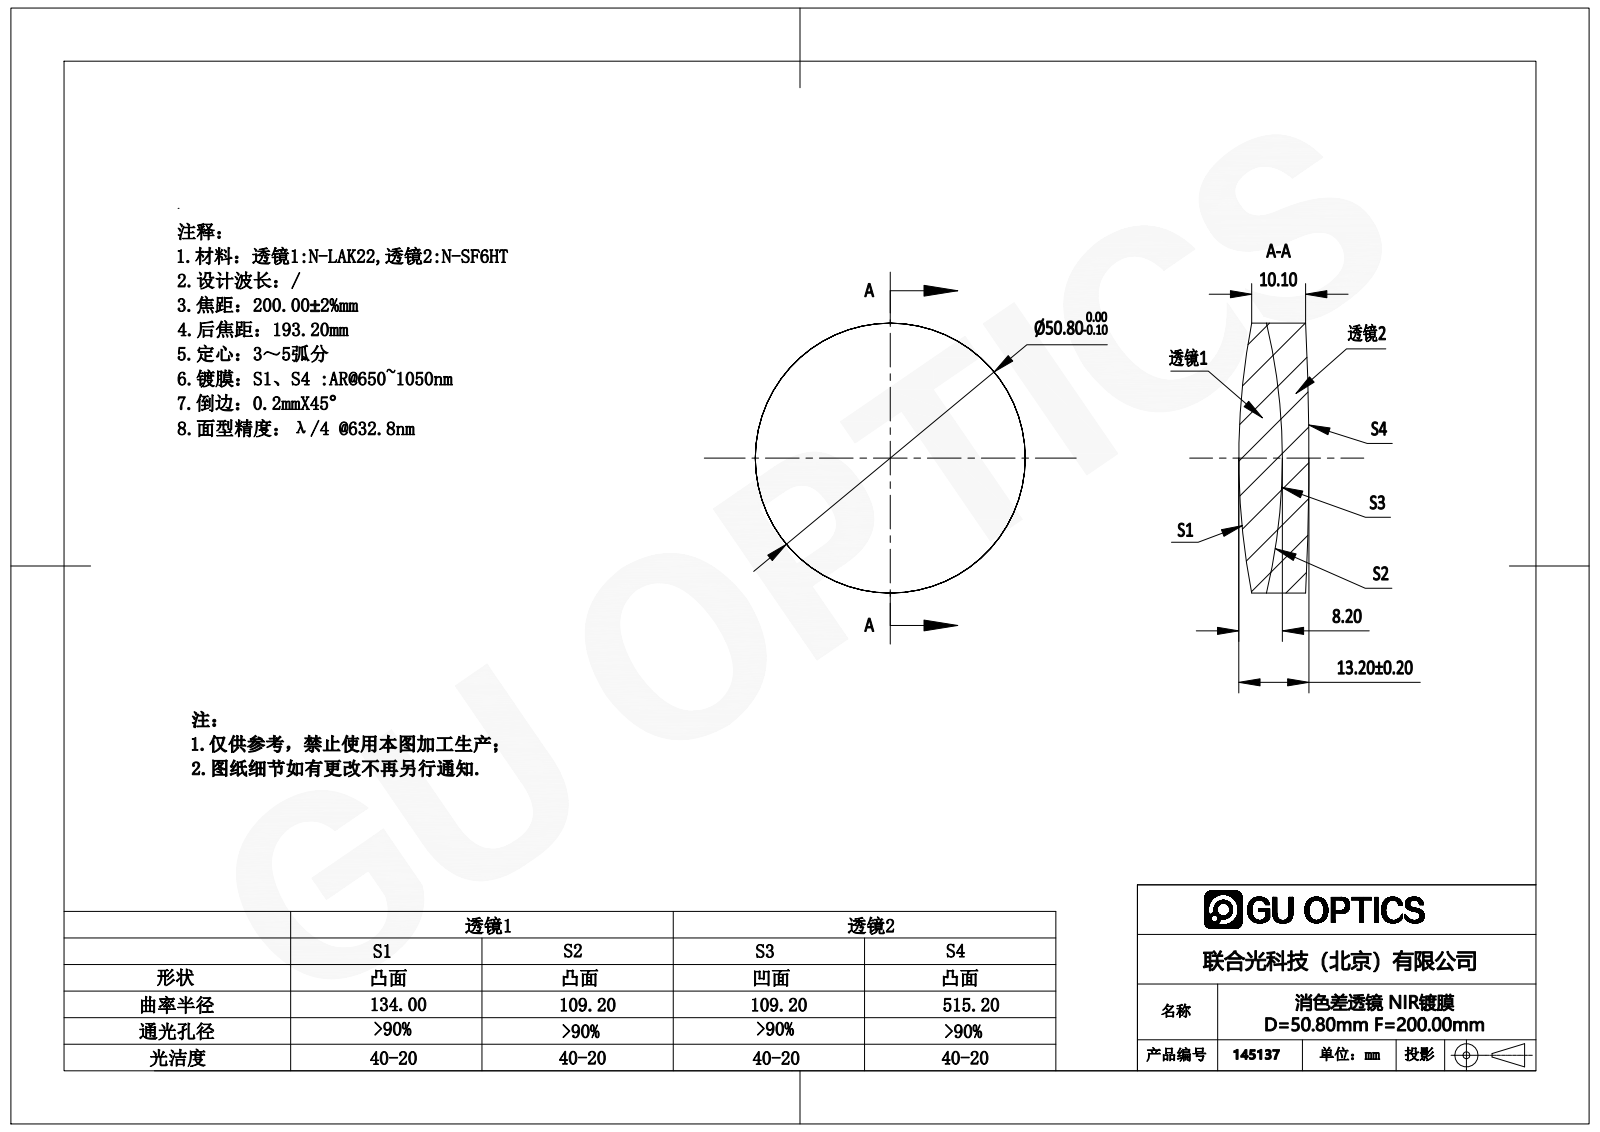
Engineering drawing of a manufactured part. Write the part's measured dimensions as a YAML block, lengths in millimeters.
part_name: "145137"
step_written_by: "SolidWorks 2016 (AUTOMOTIVE_DESIGN)"
units: millimeters
bodies: {solids: 2, faces: 12, planar: 0, cylindrical: 4, other: 8}
overall_size: [50.8, 50.8, 13.2]
volume: 23665
surface_area: 9802
round_bosses_or_shafts:
  - {diameter: 50.8, count: 1}
